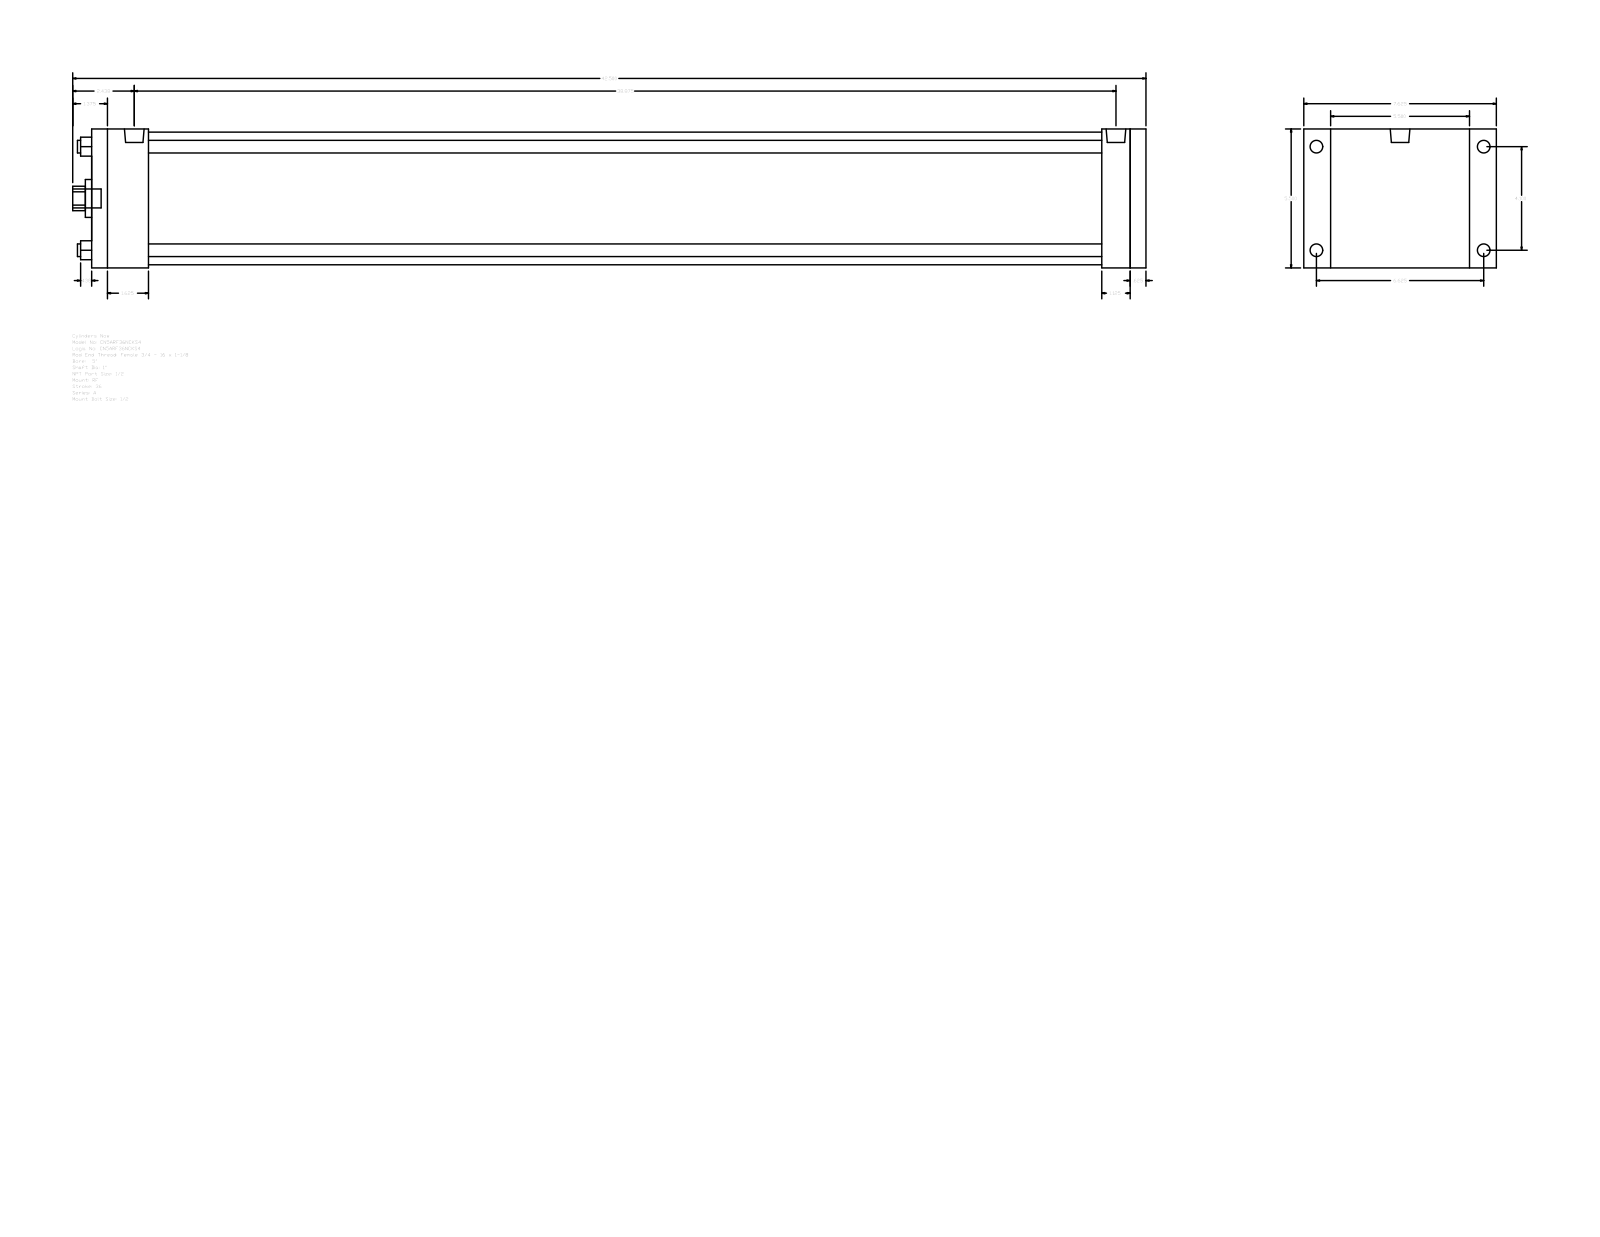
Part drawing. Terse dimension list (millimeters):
name: A_RF__0500_1
written by: GSSL Pune (CONFIG_CONTROL_DESIGN)
unit: mm
bodies: 0 solids, 92 faces (64 planar, 28 cylindrical, 0 other)
size: 1079.5 × 193.68 × 139.7
holes: 4× ⌀12.7, 1× ⌀25.4, 1× ⌀38.1, 1× ⌀133.35
bosses: 4× ⌀12.7, 4× ⌀8.73, 2× ⌀19.77, 1× ⌀19.05
rounds: 1× R12.29
face distances: 139.7, 1060.45, 1044.57, 15.88, 28.57, 57.15, 987.42, 1003.3, 1016, 958.85
hole spacings: 73.64, 104.14, 147.28
